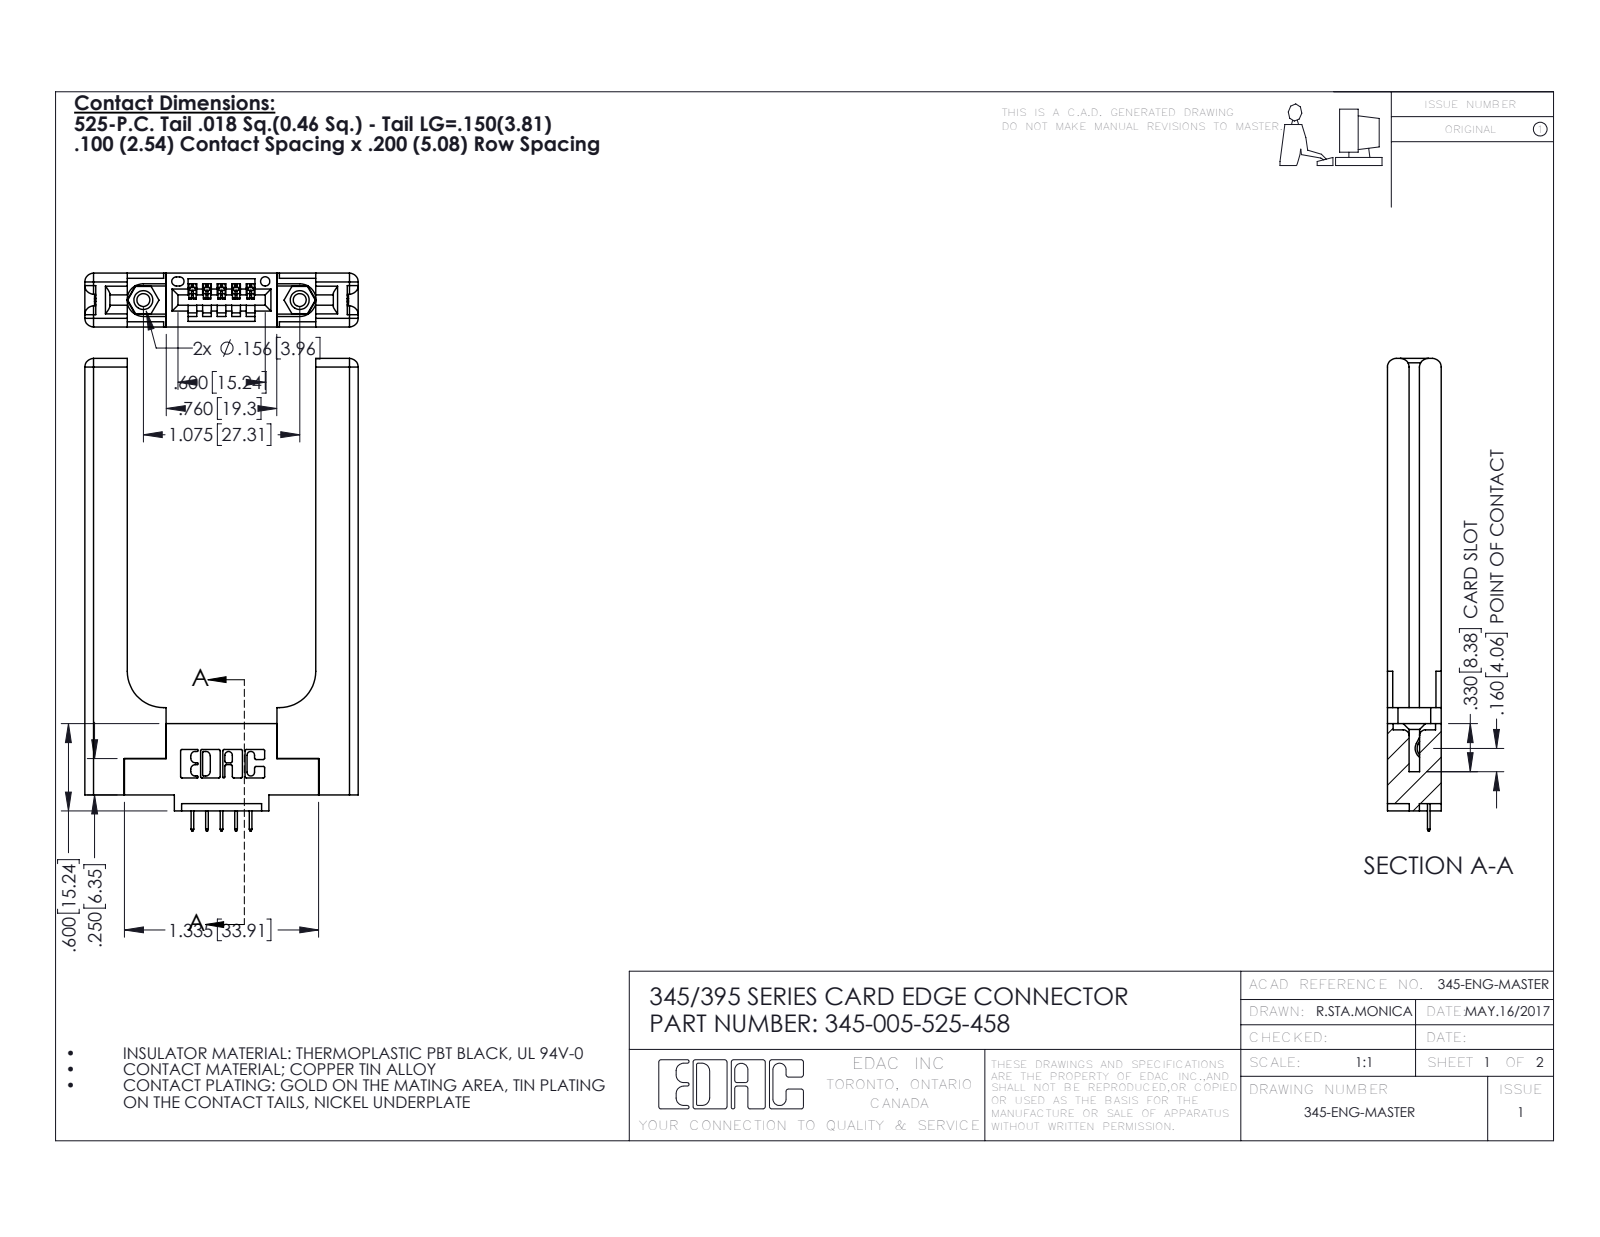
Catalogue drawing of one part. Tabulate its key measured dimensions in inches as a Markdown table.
| quantity | value |
| --- | --- |
| part name | 345-250-001_345-250-001-102; 345 Part_0.110 Offset - 0.156 Dia-TH; 345-005-525-458; 345-220-058_345-220-058 (+1 more) |
| STEP written by | SolidWorks 2020 (CONFIG_CONTROL_DESIGN) |
| units | inches |
| bodies | 10 solids, 696 faces (462 planar, 174 cylindrical, 60 other) |
| overall size | 3.247 × 1.879 × 0.37 |
| volume | 0.771 in³ |
| surface area | 15.99 in² |
| round holes (diameter × count) | 0.089 × 2, 0.125 × 2, 0.156 × 2, 0.064 × 1 |
| round bosses / shafts (diameter × count) | 0.155 × 2 |
| partial cylindrical surfaces (radius × count) | 0.01 × 22, 0.06 × 16, 0.006 × 10, 0.007 × 6, 0.031 × 6, 0.026 × 3, 0.03 × 2, 0.031 × 2 |
| main face-to-face distances | 0.37, 0.15, 0.22, 1.296, 0.072, 0.071, 0.148, 0.077, 0.292, 1.587 |
| hole center spacings | 0.27, 0.847, 1.075 |
